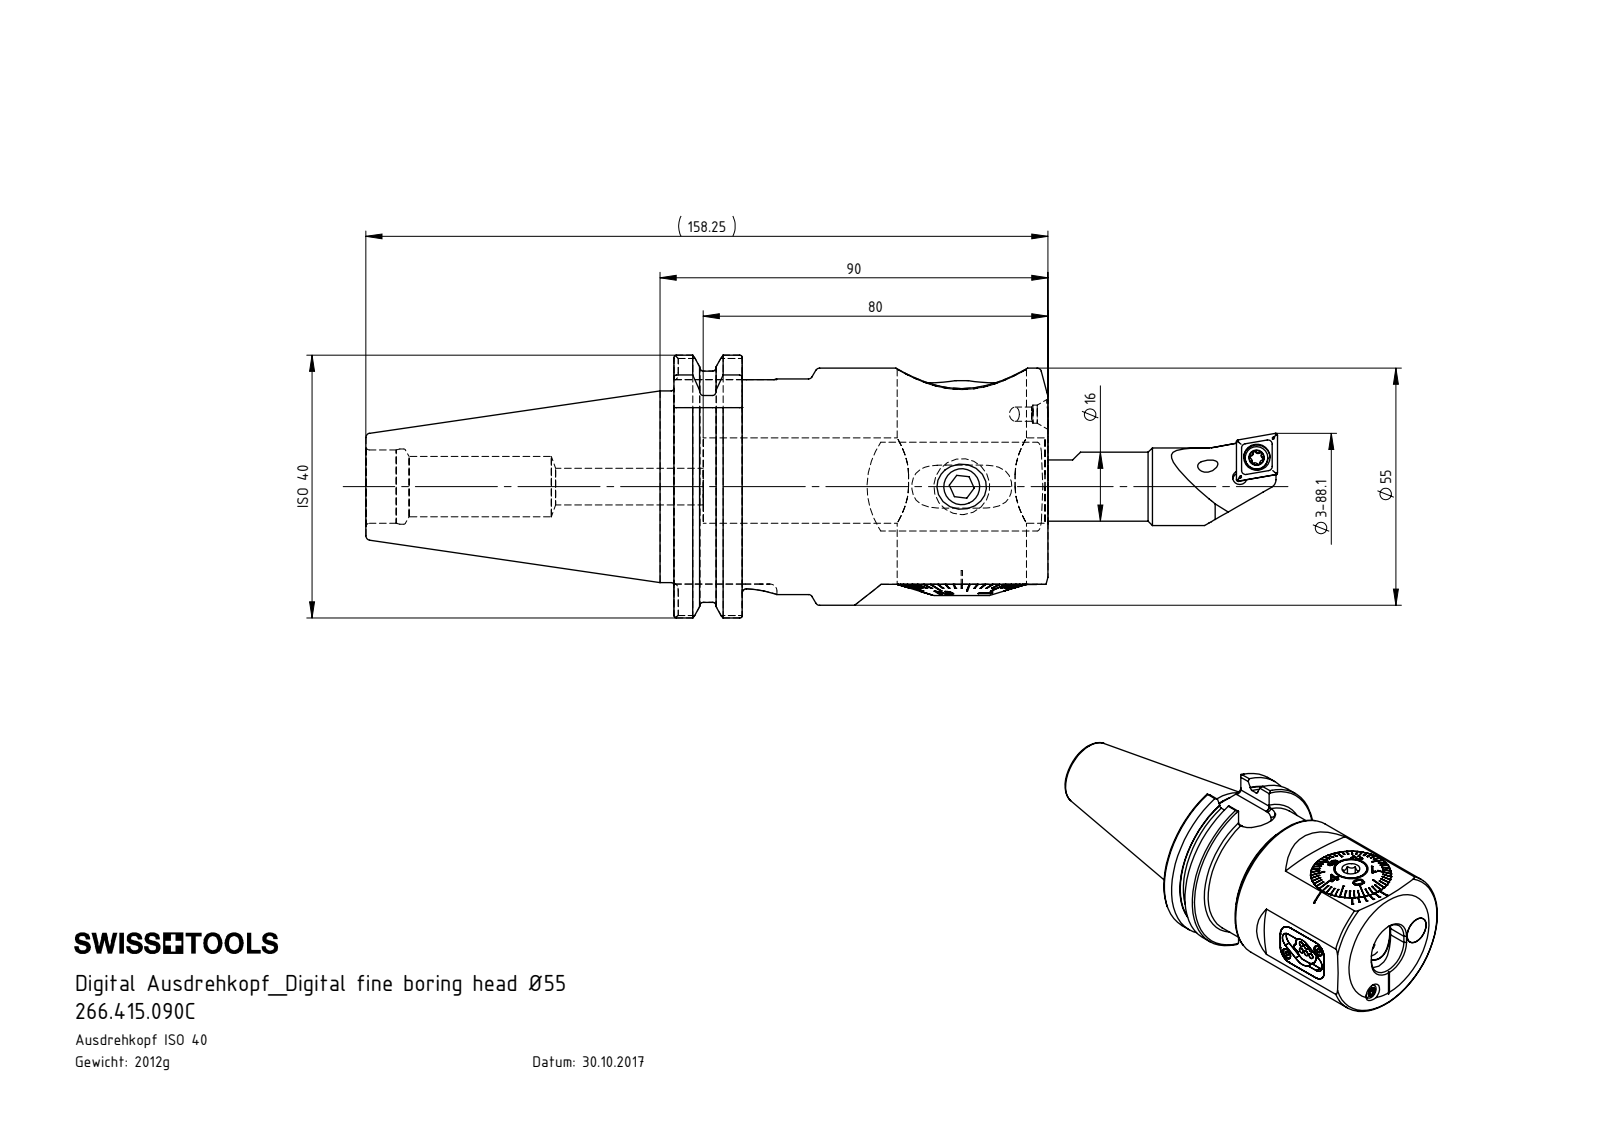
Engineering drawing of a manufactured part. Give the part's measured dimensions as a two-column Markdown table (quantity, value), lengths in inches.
| quantity | value |
| --- | --- |
| part name | A55-BG1.012.007_C; A55-BG2.012.006_B; A55-BG1.DA1.041_C_Dichtung; 266.415.090C (+8 more) |
| STEP written by | SolidWorks 2017 (CONFIG_CONTROL_DESIGN) |
| units | inches |
| bodies | 29 solids, 1284 faces (544 planar, 339 cylindrical, 401 other) |
| overall size | 8.327 × 2.5 × 2.399 |
| volume | 15.72 in³ |
| surface area | 104.9 in² |
| round holes (diameter × count) | 0.126 × 4, 0.335 × 4, 0.063 × 3, 0.13 × 3, 0.165 × 3, 0.087 × 2, 0.118 × 2, 0.551 × 2, 0.173 × 1, 0.24 × 1, 0.315 × 1, 0.394 × 1 |
| round bosses / shafts (diameter × count) | 0.075 × 6, 0.394 × 3, 0.709 × 2, 0.207 × 2, 0.157 × 2, 0.15 × 2, 0.079 × 2, 2.165 × 1 |
| partial cylindrical surfaces (radius × count) | 0.013 × 12, 0.023 × 12, 0.043 × 9, 0.047 × 8, 0.063 × 8, 0.177 × 5, 0.126 × 3, 0.173 × 3 |
| main face-to-face distances | 3.417, 0.146, 0.624, 2.793, 0.268, 0.079, 1.136, 0.157, 0.018, 0.209 |
| hole center spacings | 0.161, 0.17, 0.285, 0.333, 0.375, 0.472, 0.499, 0.571 |
